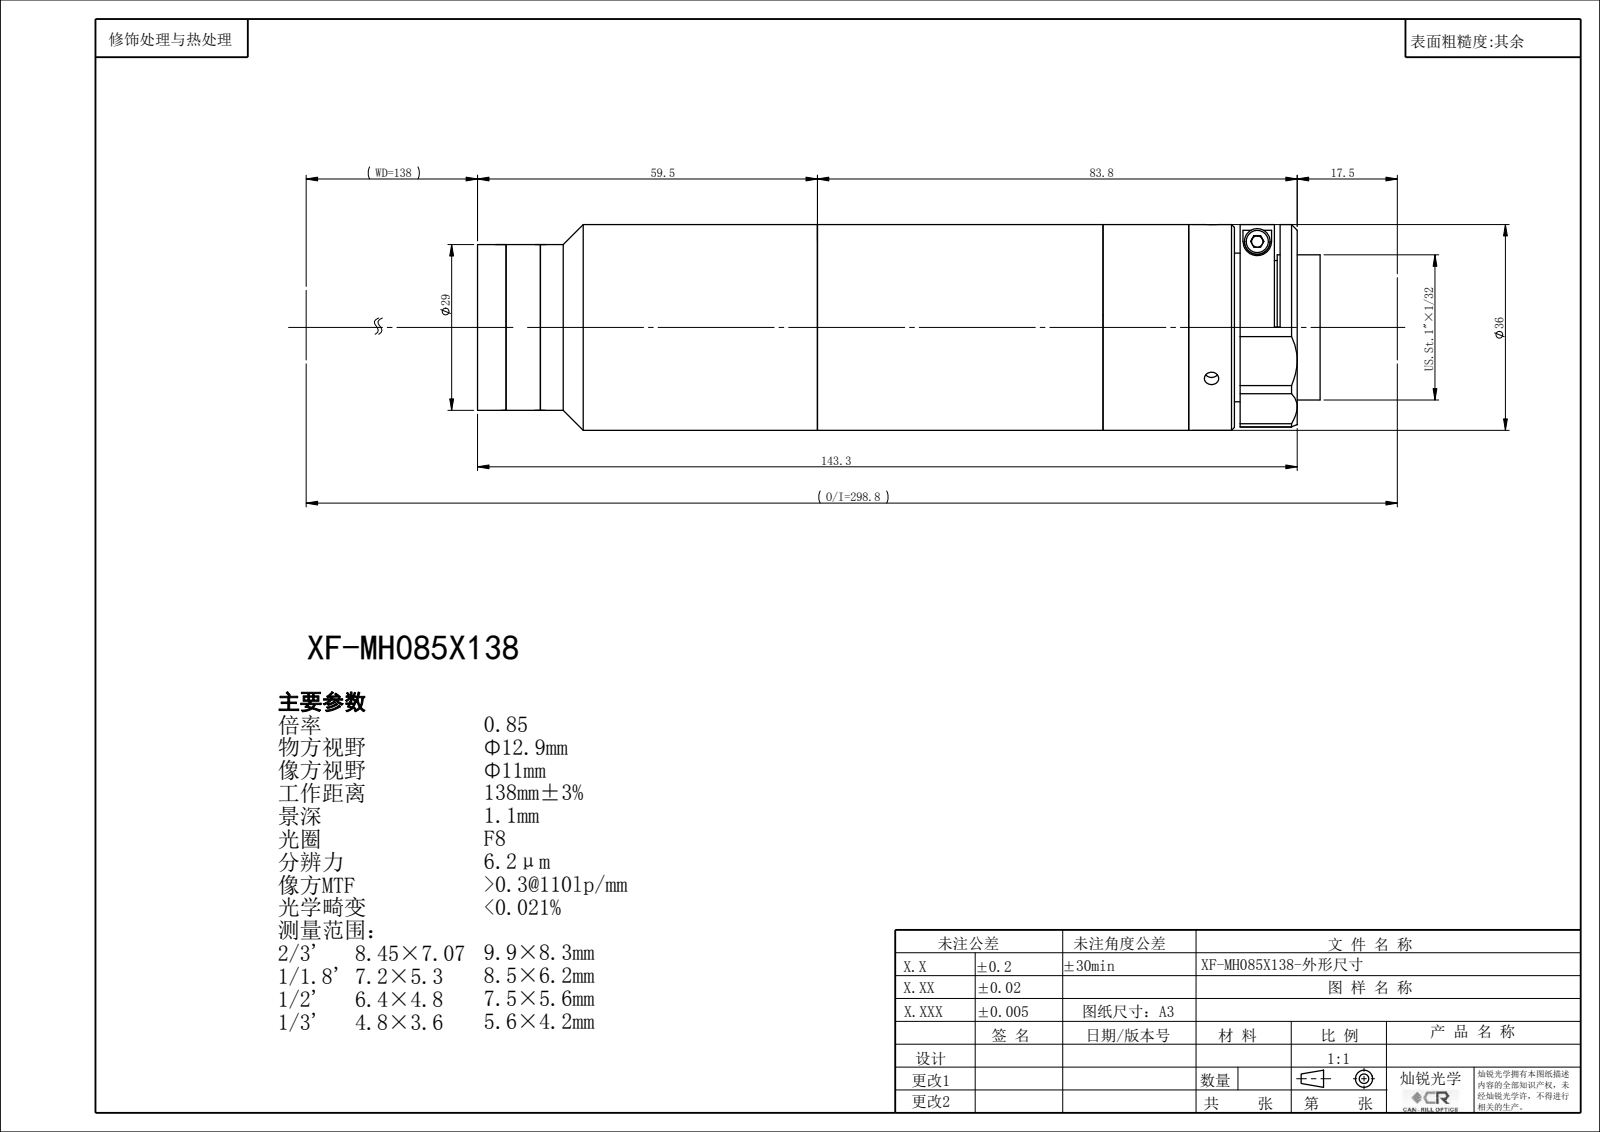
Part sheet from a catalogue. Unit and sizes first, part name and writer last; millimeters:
Units: millimetres
Overall size (bounding box): 147.24 × 36 × 36
Round holes (diameter × count): ⌀2.5 ×3, ⌀18 ×1, ⌀22.4 ×1, ⌀24 ×1, ⌀24.9 ×1, ⌀26.4 ×1
Round bosses / shafts (diameter × count): ⌀36 ×1, ⌀34 ×1, ⌀29 ×1, ⌀25.4 ×1
Main face-to-face distances: 18.74, 1.5, 17.24, 15, 32.24, 33.74, 50, 65, 82.24, 83.74
Bodies: 0 solids, 121 faces (59 planar, 40 cylindrical, 22 other)
Part name (STEP PRODUCT): XF-MH085X138
STEP written by: SolidWorks 2022 (CONFIG_CONTROL_DESIGN)
